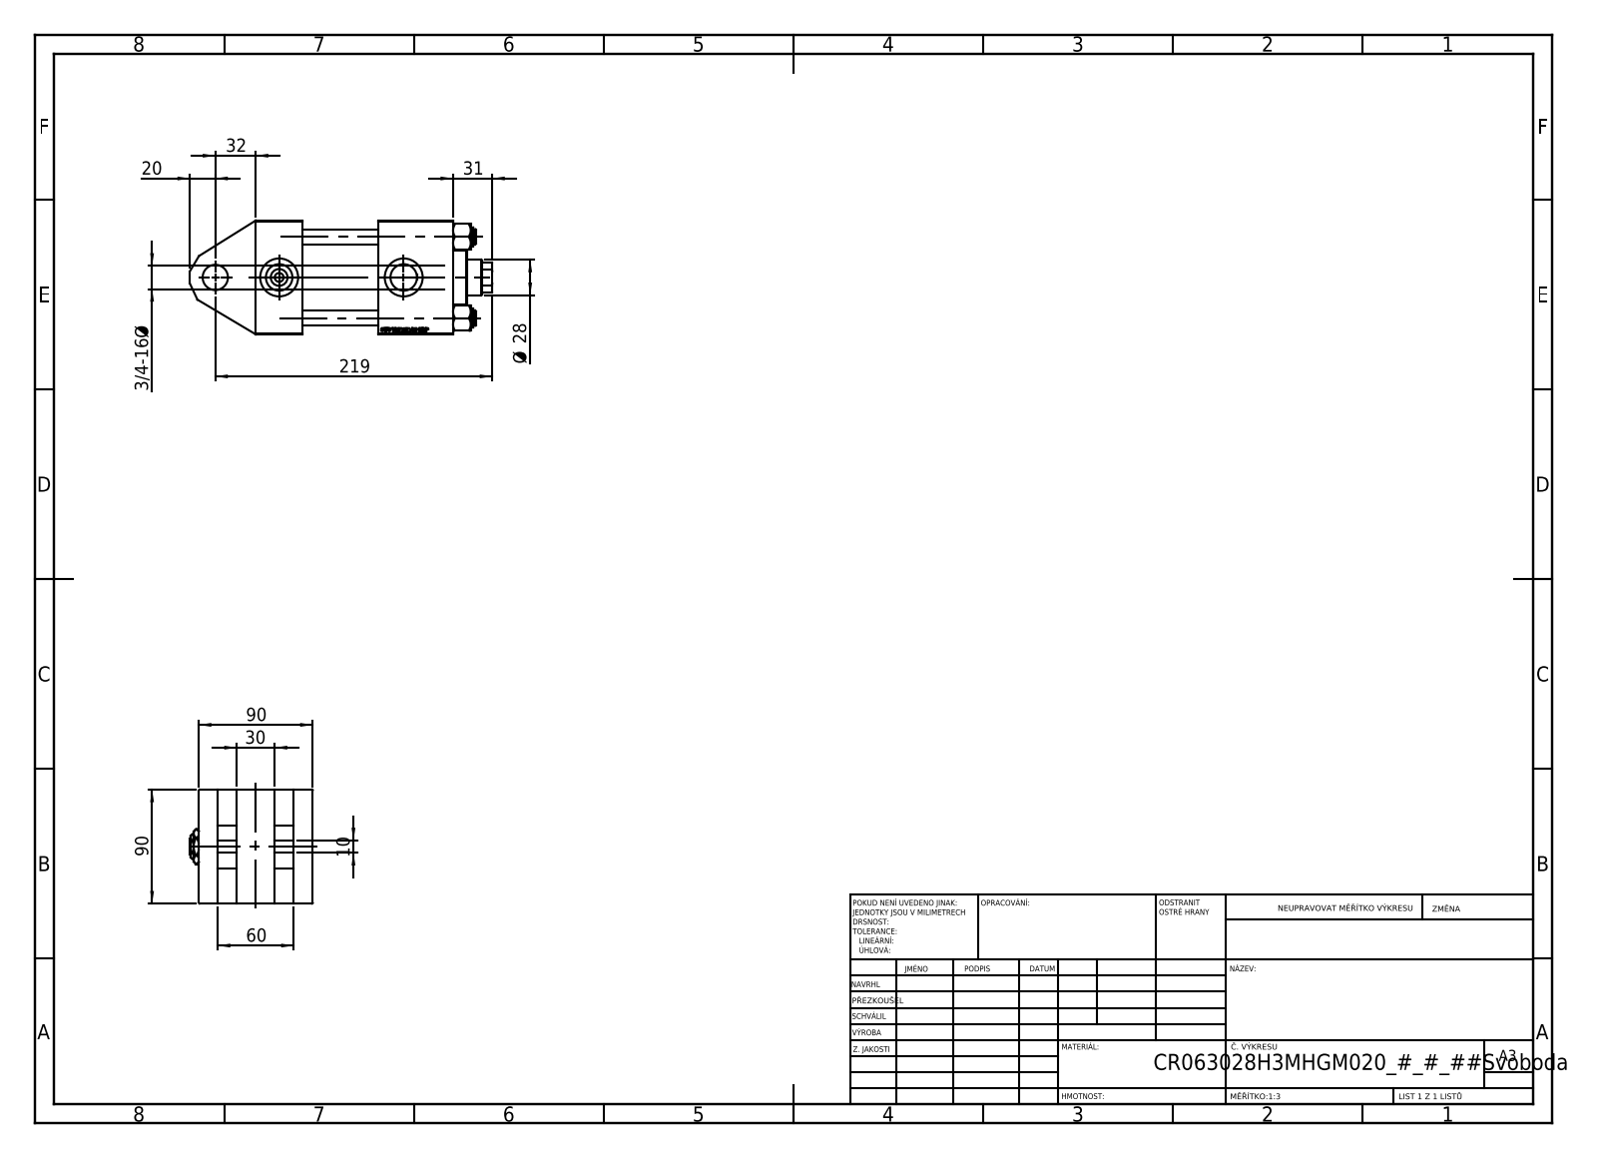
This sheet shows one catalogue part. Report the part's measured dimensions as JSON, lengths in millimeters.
{"part_name": "V215CR_TYCINKA_H; Zatka_pro_OIL_PORT; V215_VC_A; NUT_M5_H (+2 more)", "step_written_by": "SolidWorks 2019 (CONFIG_CONTROL_DESIGN)", "units": "millimeters", "bodies": {"solids": 13, "faces": 1230, "planar": 566, "cylindrical": 94, "other": 570}, "overall_size": [239, 97, 90], "volume_mm3": 1033000, "surface_area_mm2": 201962, "round_holes": [[12, 4], [7, 2], [20.96, 2], [30, 2], [18.5, 1], [20, 1], [28, 1], [31, 1], [50, 1], [60, 1], [63, 1]], "round_bosses_or_shafts": [[15, 4], [69, 1], [42, 1]], "partial_cylinders_radius": [[13.5, 1]], "face_to_face_distances": [90, 60, 15, 30, 119, 37, 75, 156, 45, 97], "hole_center_spacings": [45.47, 64.3, 90.93, 50.5, 98.5, 149]}
